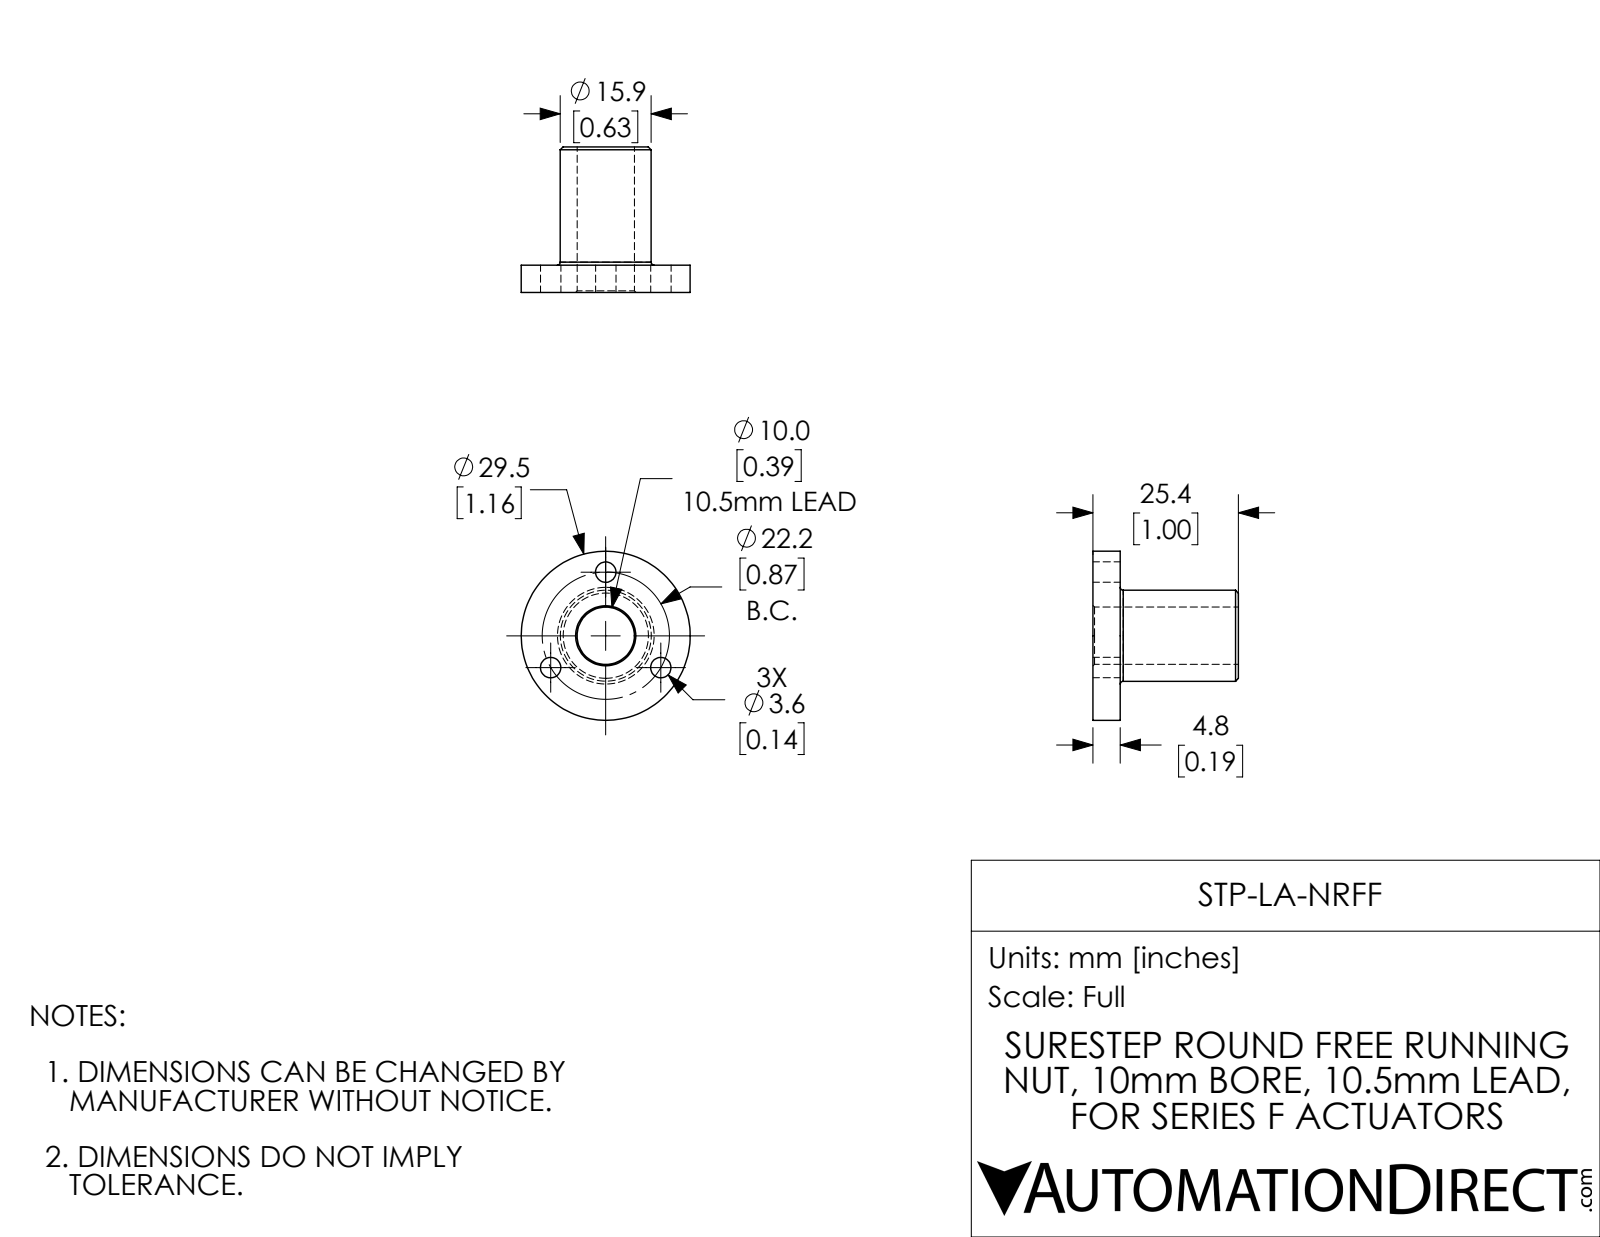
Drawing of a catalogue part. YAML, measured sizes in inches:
part_name: "STP-LA-NRFF"
step_written_by: "SolidWorks 2017 (AUTOMOTIVE_DESIGN)"
units: inches
bodies: {solids: 1, faces: 21, planar: 3, cylindrical: 12, other: 6}
overall_size: [1.161, 1.161, 1]
volume: 0.317
surface_area: 5.501
round_holes:
  - {diameter: 0.14, count: 3}
  - {diameter: 0.394, count: 1}
round_bosses_or_shafts:
  - {diameter: 1.161, count: 1}
  - {diameter: 0.625, count: 1}
face_to_face_distances: [0.187, 0.813, 1]
hole_center_spacings: [0.437, 0.757, 0.758]
